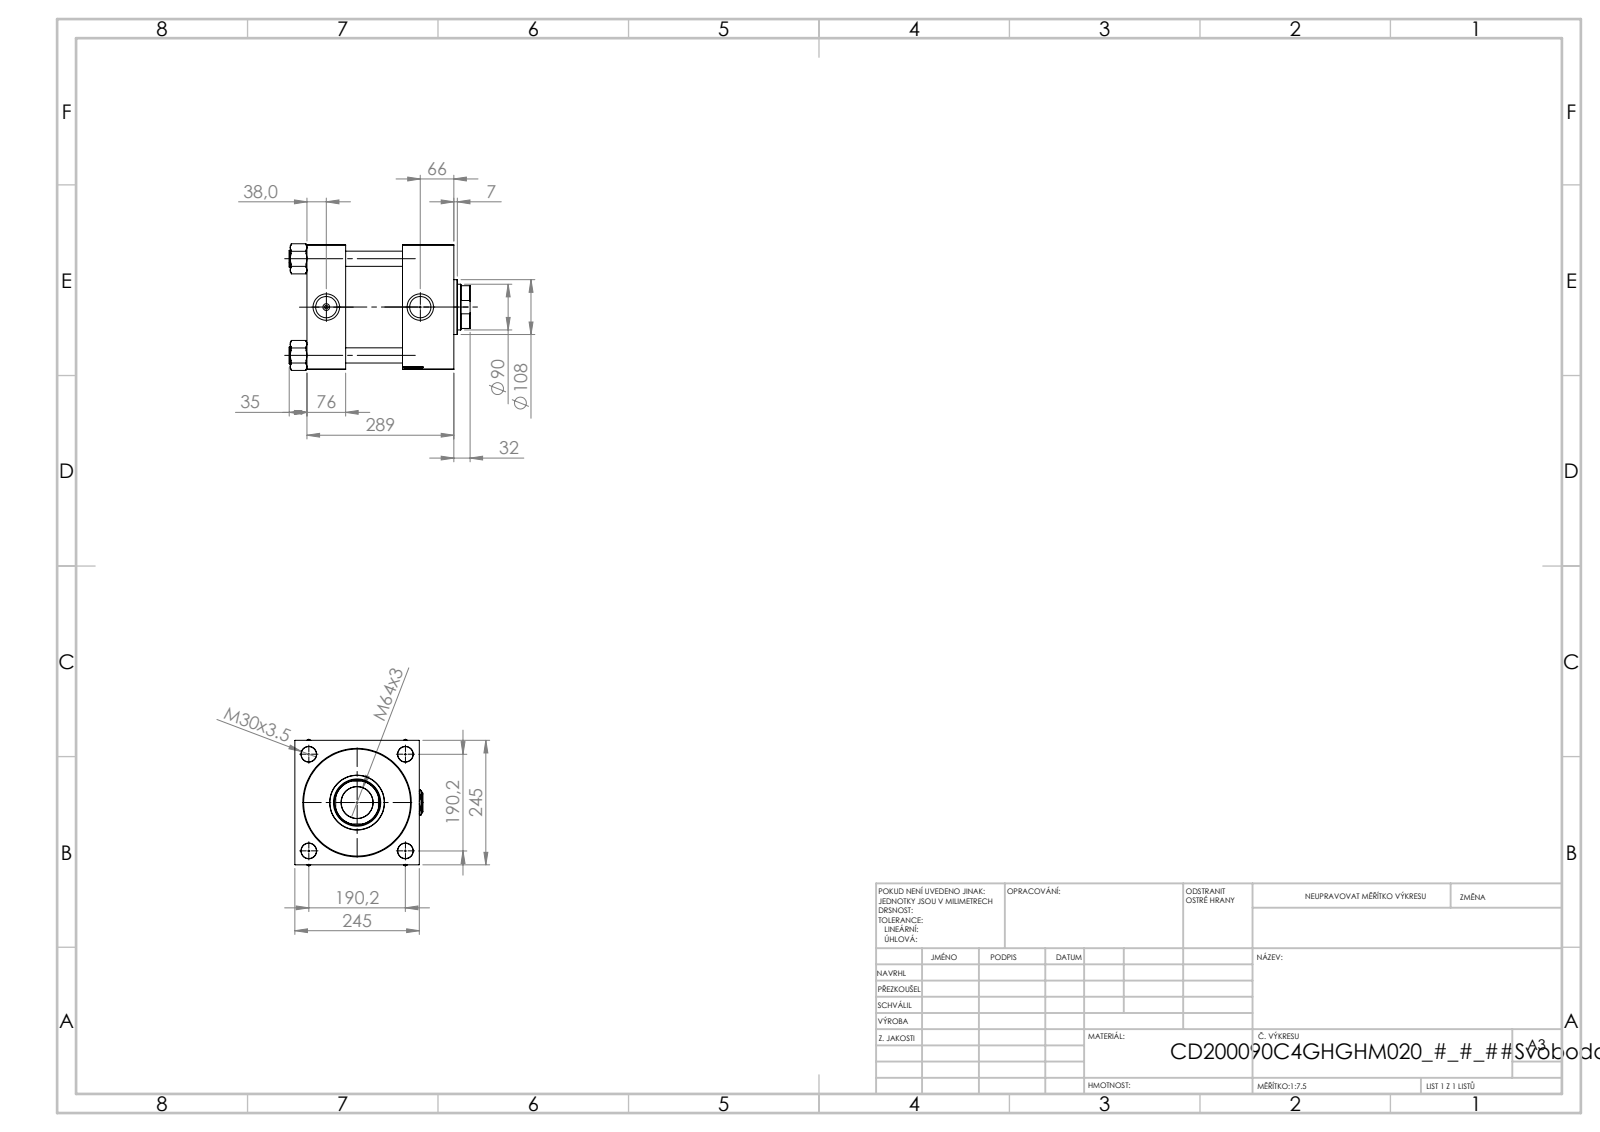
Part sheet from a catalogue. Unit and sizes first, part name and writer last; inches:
Units: inches
Overall size (bounding box): 14.016 × 9.921 × 9.82
Round holes (diameter × count): ⌀1.181 ×4, ⌀0.276 ×2, ⌀1.65 ×2, ⌀2.047 ×2, ⌀2.461 ×1, ⌀3.543 ×1, ⌀3.661 ×1, ⌀5.748 ×1, ⌀7.874 ×1, ⌀8.287 ×1
Round bosses / shafts (diameter × count): ⌀1.299 ×4, ⌀8.11 ×1, ⌀4.252 ×1
Partial cylindrical surfaces — rounded edges, fillets, slot ends (radius × count): R1.732 ×1
Main face-to-face distances: 9.646, 2.992, 11.378, 8.386, 10.248, 7.256, 1.13, 7.402, 4.409, 2.846
Hole centre spacings: 5.295, 7.488, 10.59, 7.283
Volume: 816.5 in³ · Surface area: 1 624 in²
Bodies: 12 solids, 1243 faces (597 planar, 90 cylindrical, 556 other)
Part name (STEP PRODUCT): NUT_M5_V215CD_C; V215CD_VC_C; V215CD_C_TYCINKA; Zatka_pro_OIL_PORT (+2 more)
STEP written by: SolidWorks 2019 (CONFIG_CONTROL_DESIGN)
